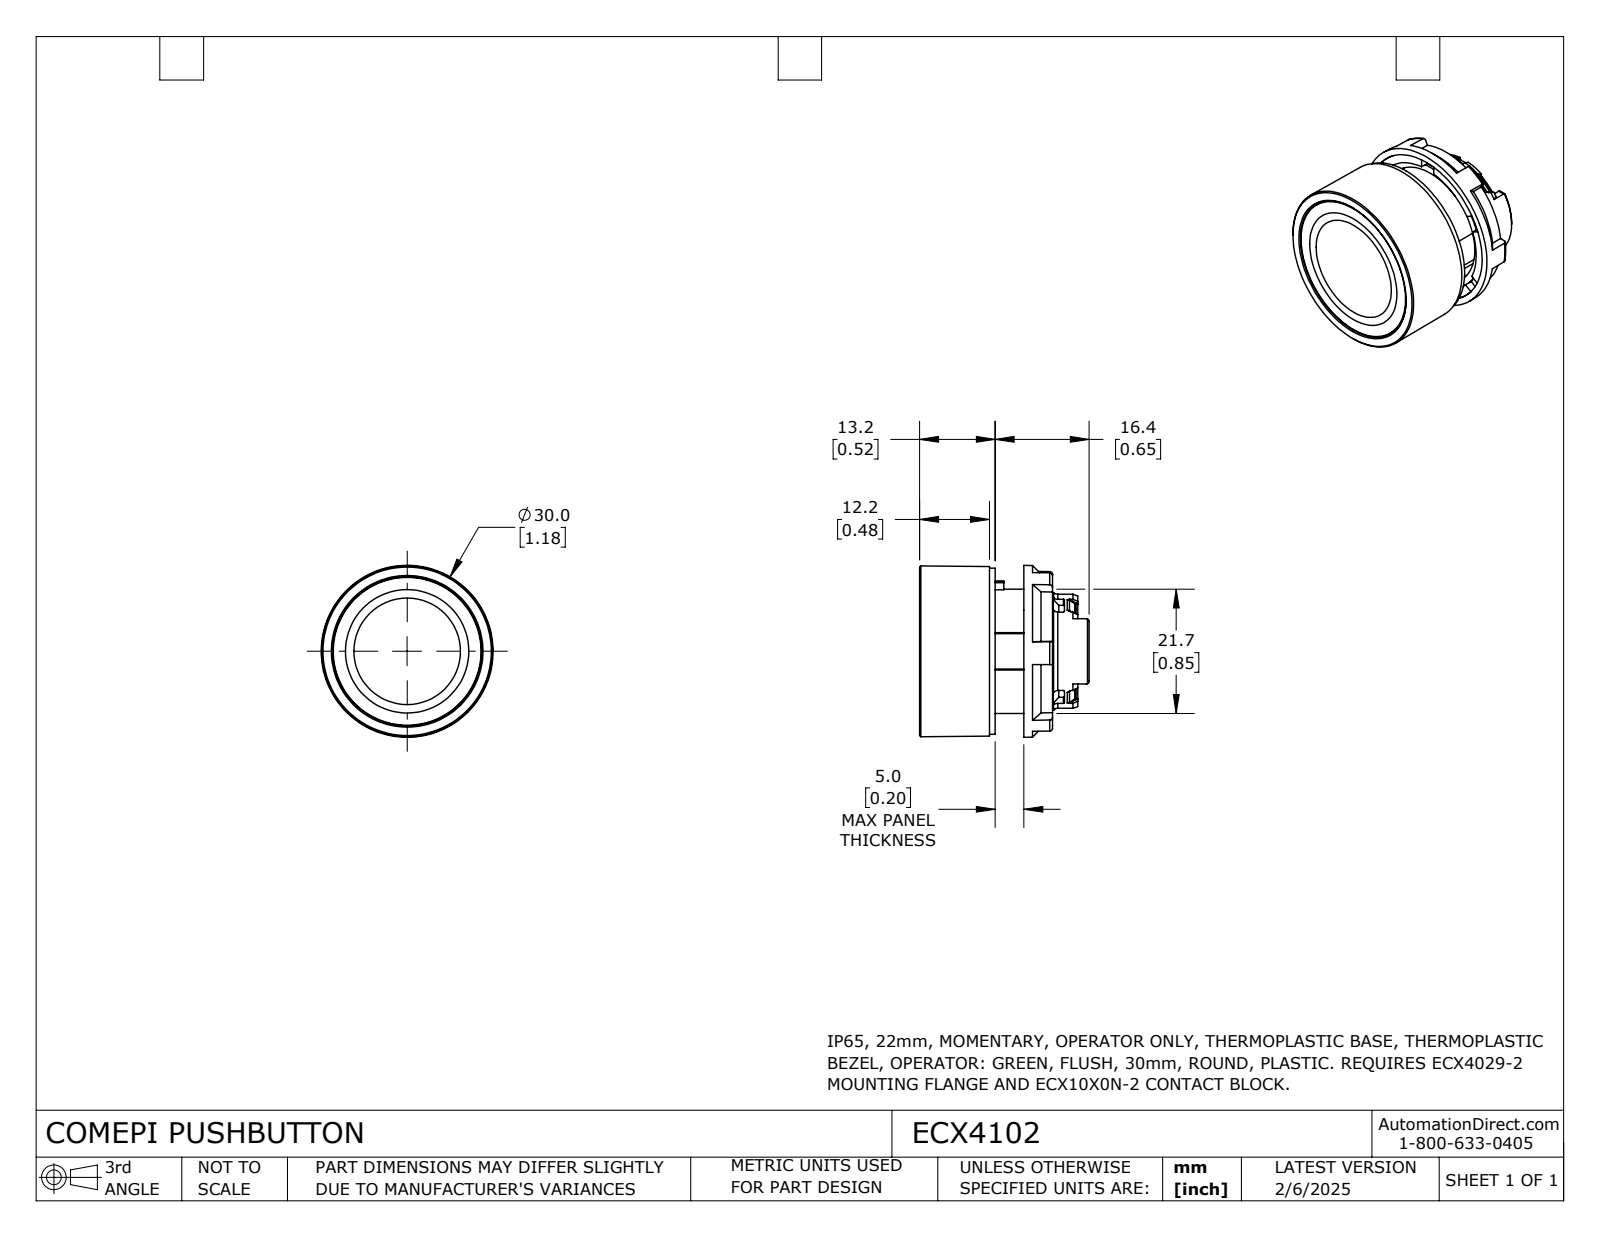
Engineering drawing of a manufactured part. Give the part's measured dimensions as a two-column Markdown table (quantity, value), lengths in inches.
| quantity | value |
| --- | --- |
| part name | ECX4102 |
| STEP written by | SolidWorks 2024 (CONFIG_CONTROL_DESIGN) |
| units | inches |
| bodies | 3 solids, 398 faces (134 planar, 111 cylindrical, 153 other) |
| overall size | 1.181 × 1.181 × 1.165 |
| volume | 0.472 in³ |
| surface area | 16.55 in² |
| round holes (diameter × count) | 0.531 × 1, 0.713 × 1, 0.866 × 1 |
| round bosses / shafts (diameter × count) | 1.142 × 1, 1.016 × 1, 0.965 × 1, 0.854 × 1, 0.807 × 1, 0.787 × 1, 0.748 × 1, 0.728 × 1 |
| partial cylindrical surfaces (radius × count) | 0.008 × 24, 0.02 × 8, 0.01 × 2, 0.293 × 1, 0.344 × 1, 0.348 × 1, 0.366 × 1 |
| main face-to-face distances | 0.409, 0.039, 0.433, 0.472, 0.236, 0.394, 0.197, 0.449, 0.512, 0.217 |
